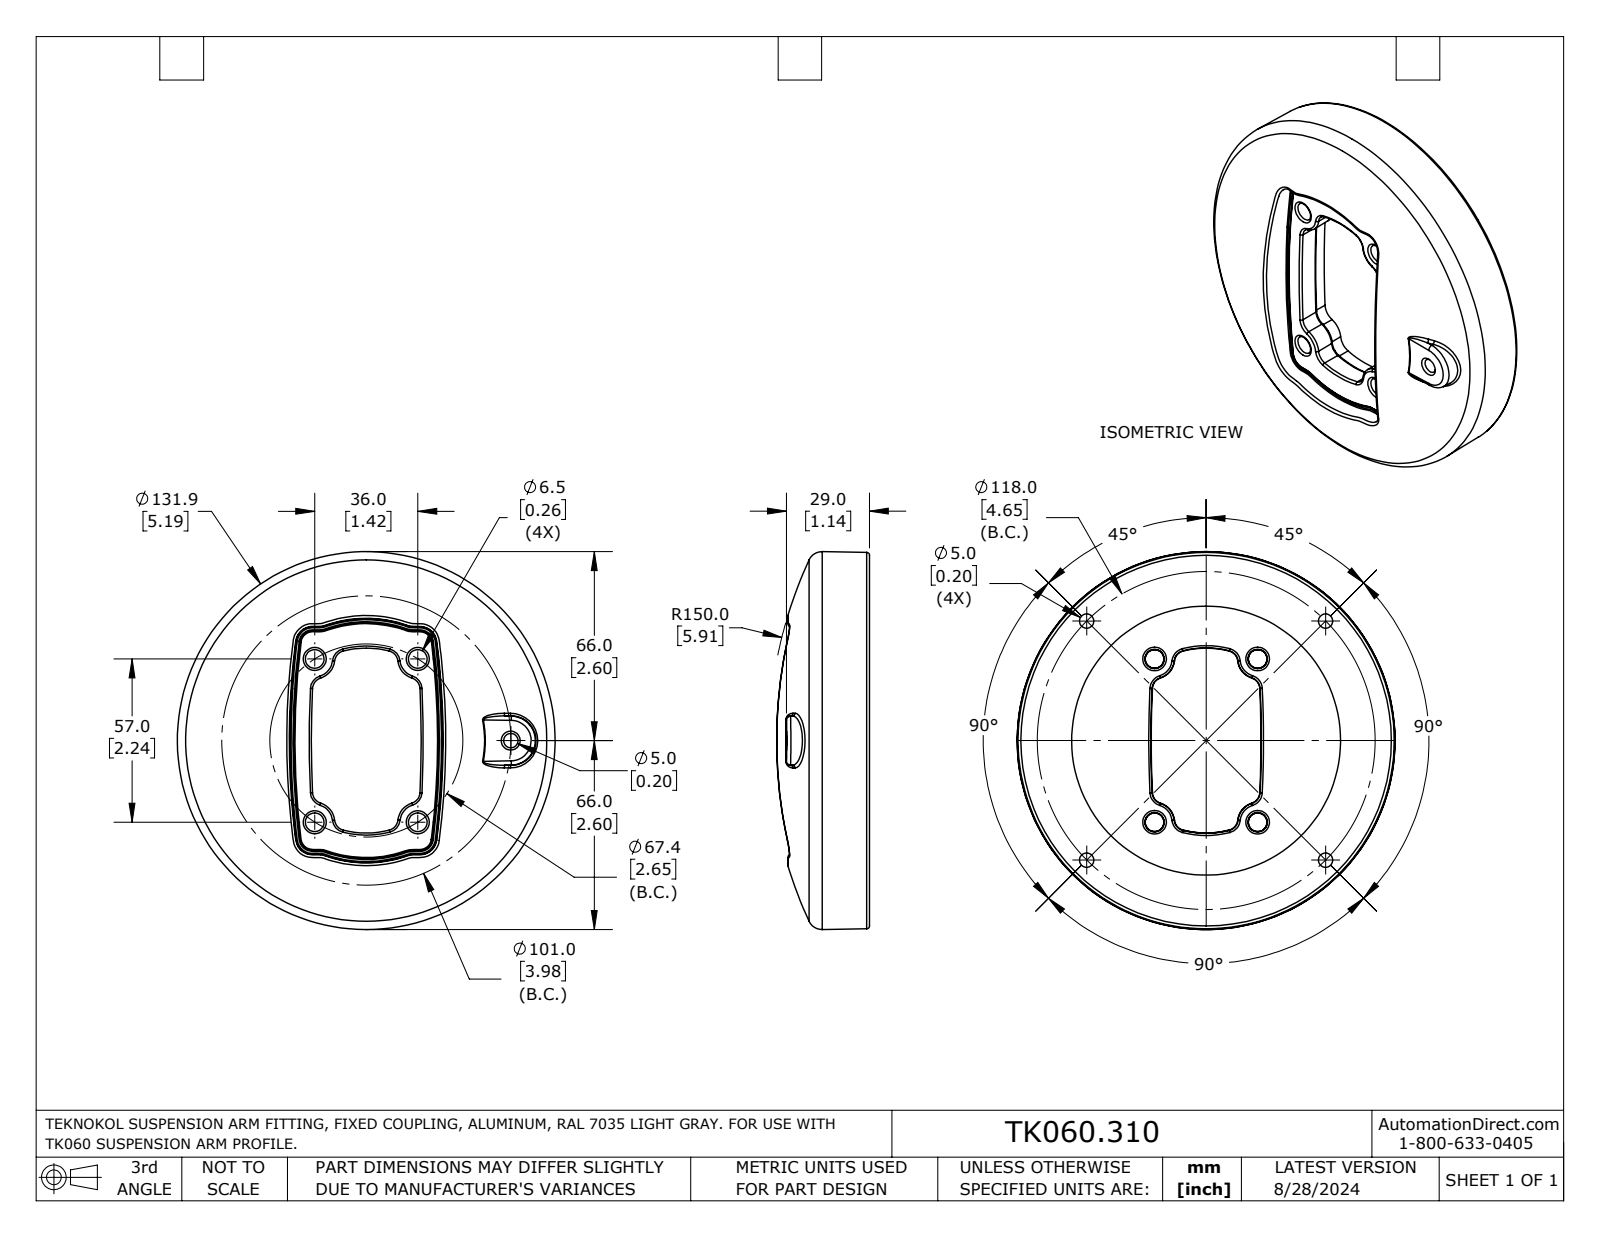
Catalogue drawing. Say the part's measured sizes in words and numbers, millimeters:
The part is named "TK060.310". Its 3-D file was written by "SolidWorks 2023 (AUTOMOTIVE_DESIGN)". It is 1 solid with 419 faces: 67 planar, 51 cylindrical and 301 other. Overall it measures 131.9 by 131.9 by 32.4 millimeters. Its volume is 218 300 cubic millimeters and its surface area 54 090 square millimeters. Round holes: 4 of diameter 5, 4 of diameter 8.3, 1 of diameter 93.9. Partial cylindrical surfaces (rounded edges, fillets, slot ends): 18 of radius 1.5, 8 of radius 4.9, 6 of radius 1, 4 of radius 6.1, 2 of radius 1.2, 2 of radius 395.5, 1 of radius 33.1. The main face-to-face distances are 10, 4.5, 14.5, 8, 22.5, 12.5, 17.5, 7.5, 3, 5. The hole center spacings are 27.2, 33.7, 59, 61.2, 74.1, 83.4, 92.2, 36.
